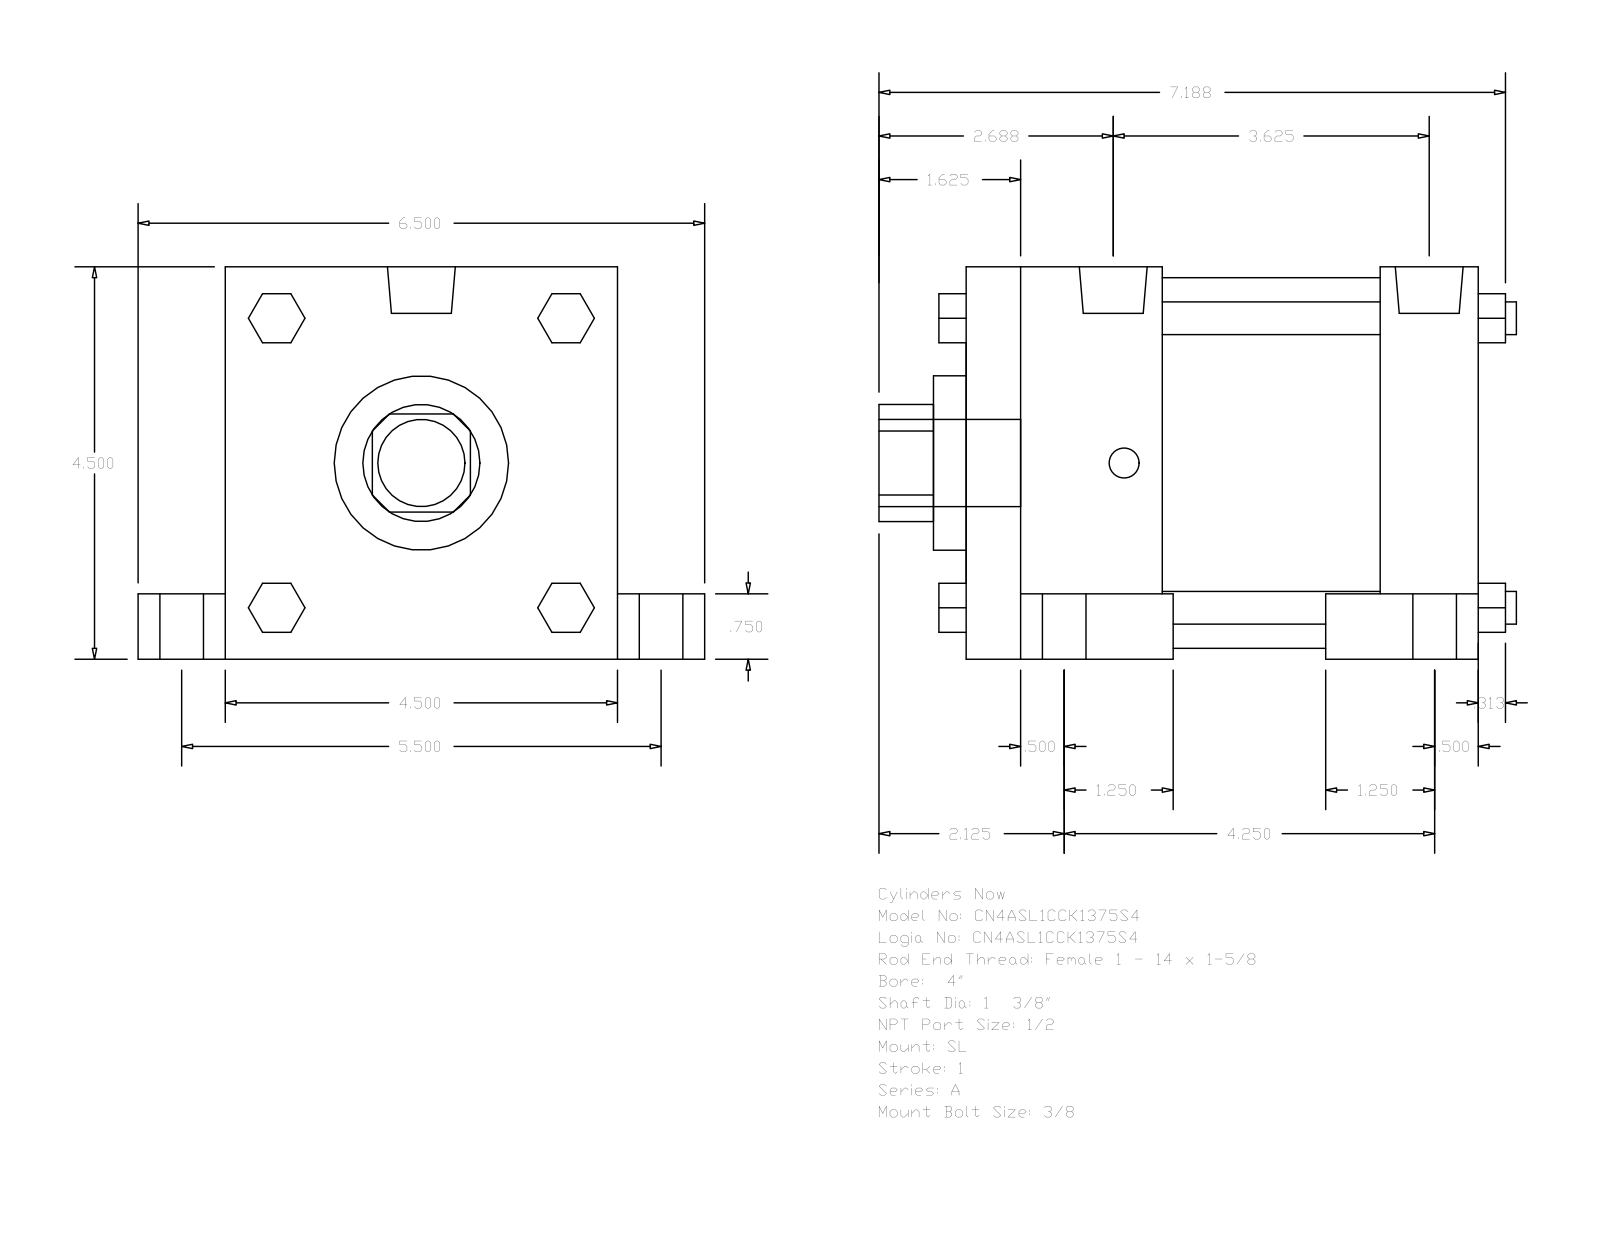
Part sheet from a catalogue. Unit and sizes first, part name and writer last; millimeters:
Units: millimetres
Overall size (bounding box): 185.74 × 165.1 × 114.3
Round holes (diameter × count): ⌀34.92 ×1, ⌀50.8 ×1, ⌀107.95 ×1
Round bosses / shafts (diameter × count): ⌀19.05 ×4, ⌀12.7 ×4, ⌀9.53 ×4, ⌀8.73 ×4, ⌀19.77 ×2, ⌀25.4 ×1
Partial cylindrical surfaces — rounded edges, fillets, slot ends (radius × count): R17.06 ×1
Main face-to-face distances: 114.3, 149.22, 28.57, 25.4, 57.15, 92.07, 120.65, 63.5, 139.7, 19.05
Bodies: 0 solids, 150 faces (114 planar, 36 cylindrical, 0 other)
Part name (STEP PRODUCT): A_SL__0400_1.375
STEP written by: GSSL Pune (CONFIG_CONTROL_DESIGN)
